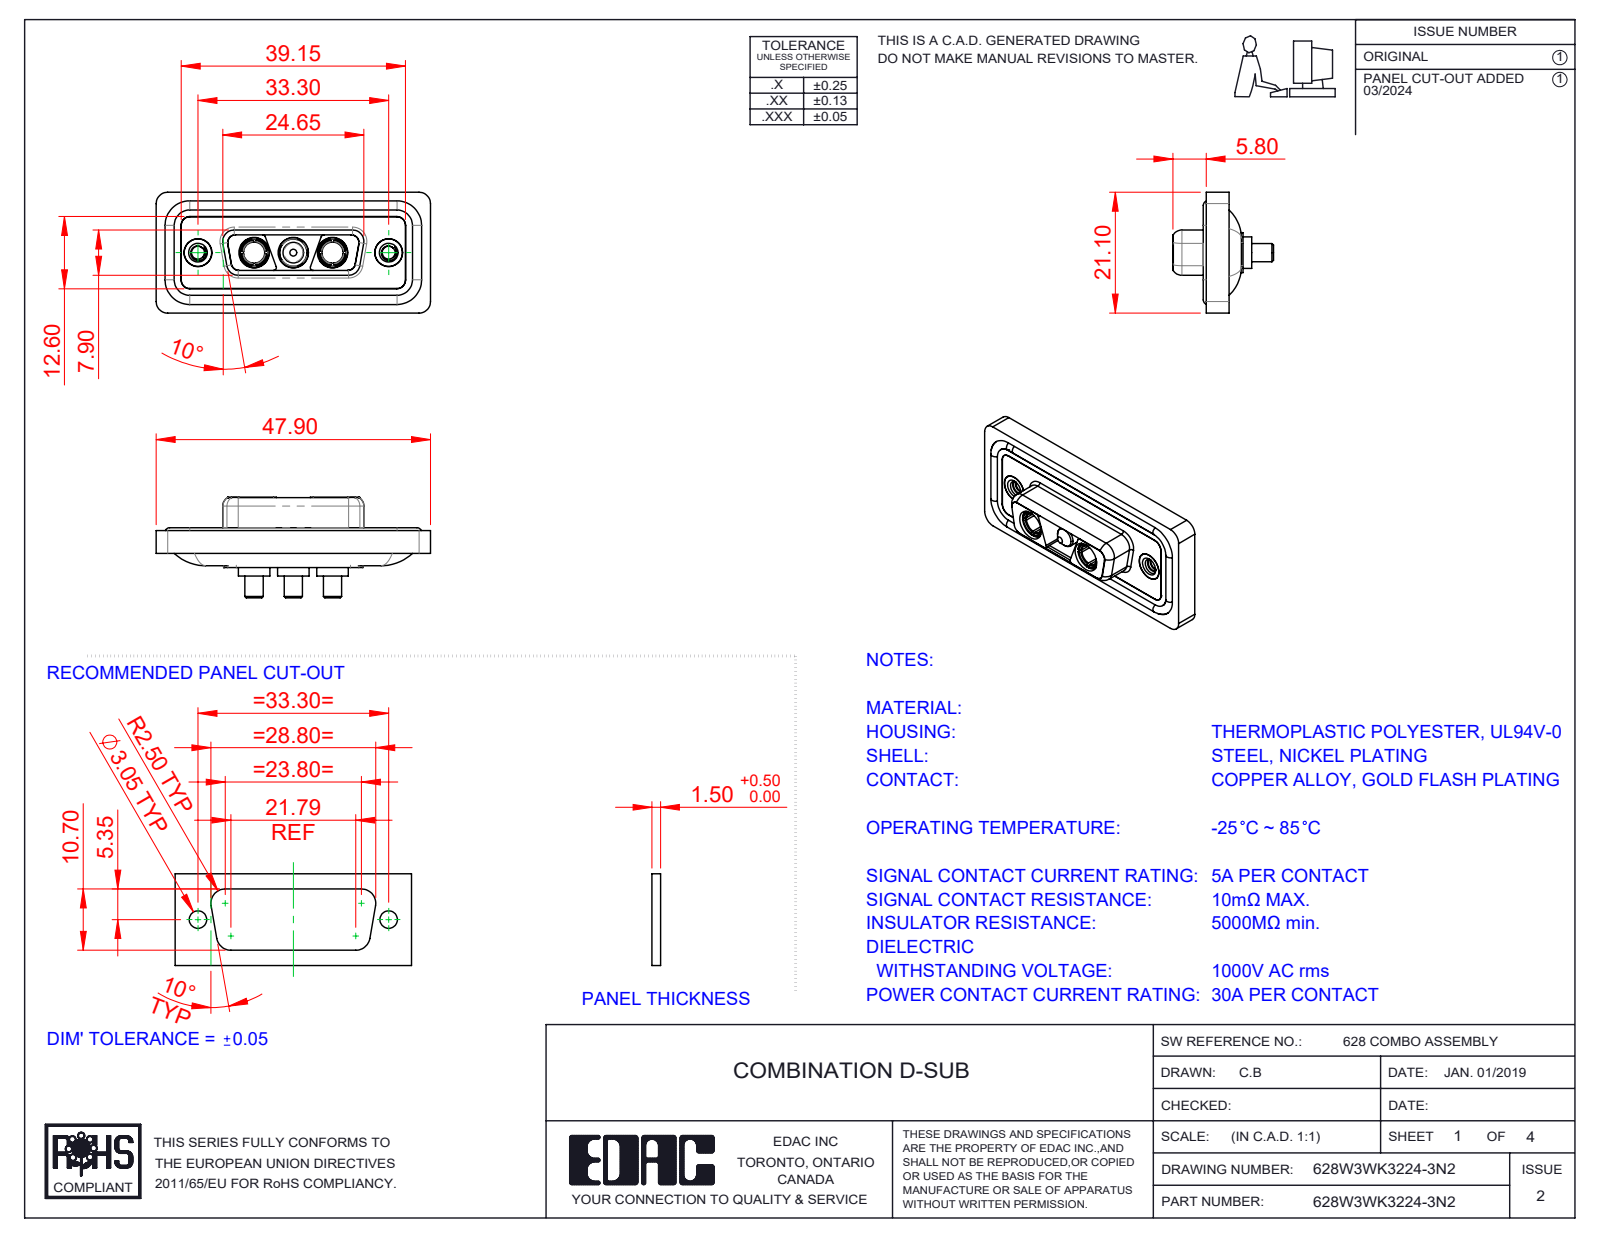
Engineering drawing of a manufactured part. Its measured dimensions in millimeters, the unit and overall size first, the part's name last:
Units: millimetres
Overall size (bounding box): 47.9 × 21.1 × 17.55
Round holes (diameter × count): ⌀4.85 ×5, ⌀5.3 ×3, ⌀2.26 ×2, ⌀3.7 ×2, ⌀4 ×2, ⌀4.05 ×2, ⌀5 ×2
Round bosses / shafts (diameter × count): ⌀1.6 ×4, ⌀5.5 ×3, ⌀5.2 ×3, ⌀4.75 ×3, ⌀3.75 ×3, ⌀3.2 ×3, ⌀4.96 ×2, ⌀4.95 ×2
Partial cylindrical surfaces — rounded edges, fillets, slot ends (radius × count): R1.5 ×22, R2 ×20, R1.35 ×12, R0.5 ×8, R1.6 ×8, R0.25 ×4, R0.6 ×4, R0.65 ×4
Main face-to-face distances: 0.4, 1.6, 0.5, 1.8, 1.1, 2.9, 5.65, 7.05, 5.35, 1.5
Hole centre spacings: 6.85, 9.8, 16.65, 23.5, 13.7, 33.3
Volume: 5 899 mm³ · Surface area: 9 518 mm²
Bodies: 13 solids, 583 faces (178 planar, 258 cylindrical, 147 other)
Part name (STEP PRODUCT): Power Pin_30A S; 628W3WK3224-3N2; 628Combo Shell Front_15 Contacts; 628Combo Threaded Rivet_2 (+4 more)
STEP written by: SolidWorks 2023 (CONFIG_CONTROL_DESIGN)
